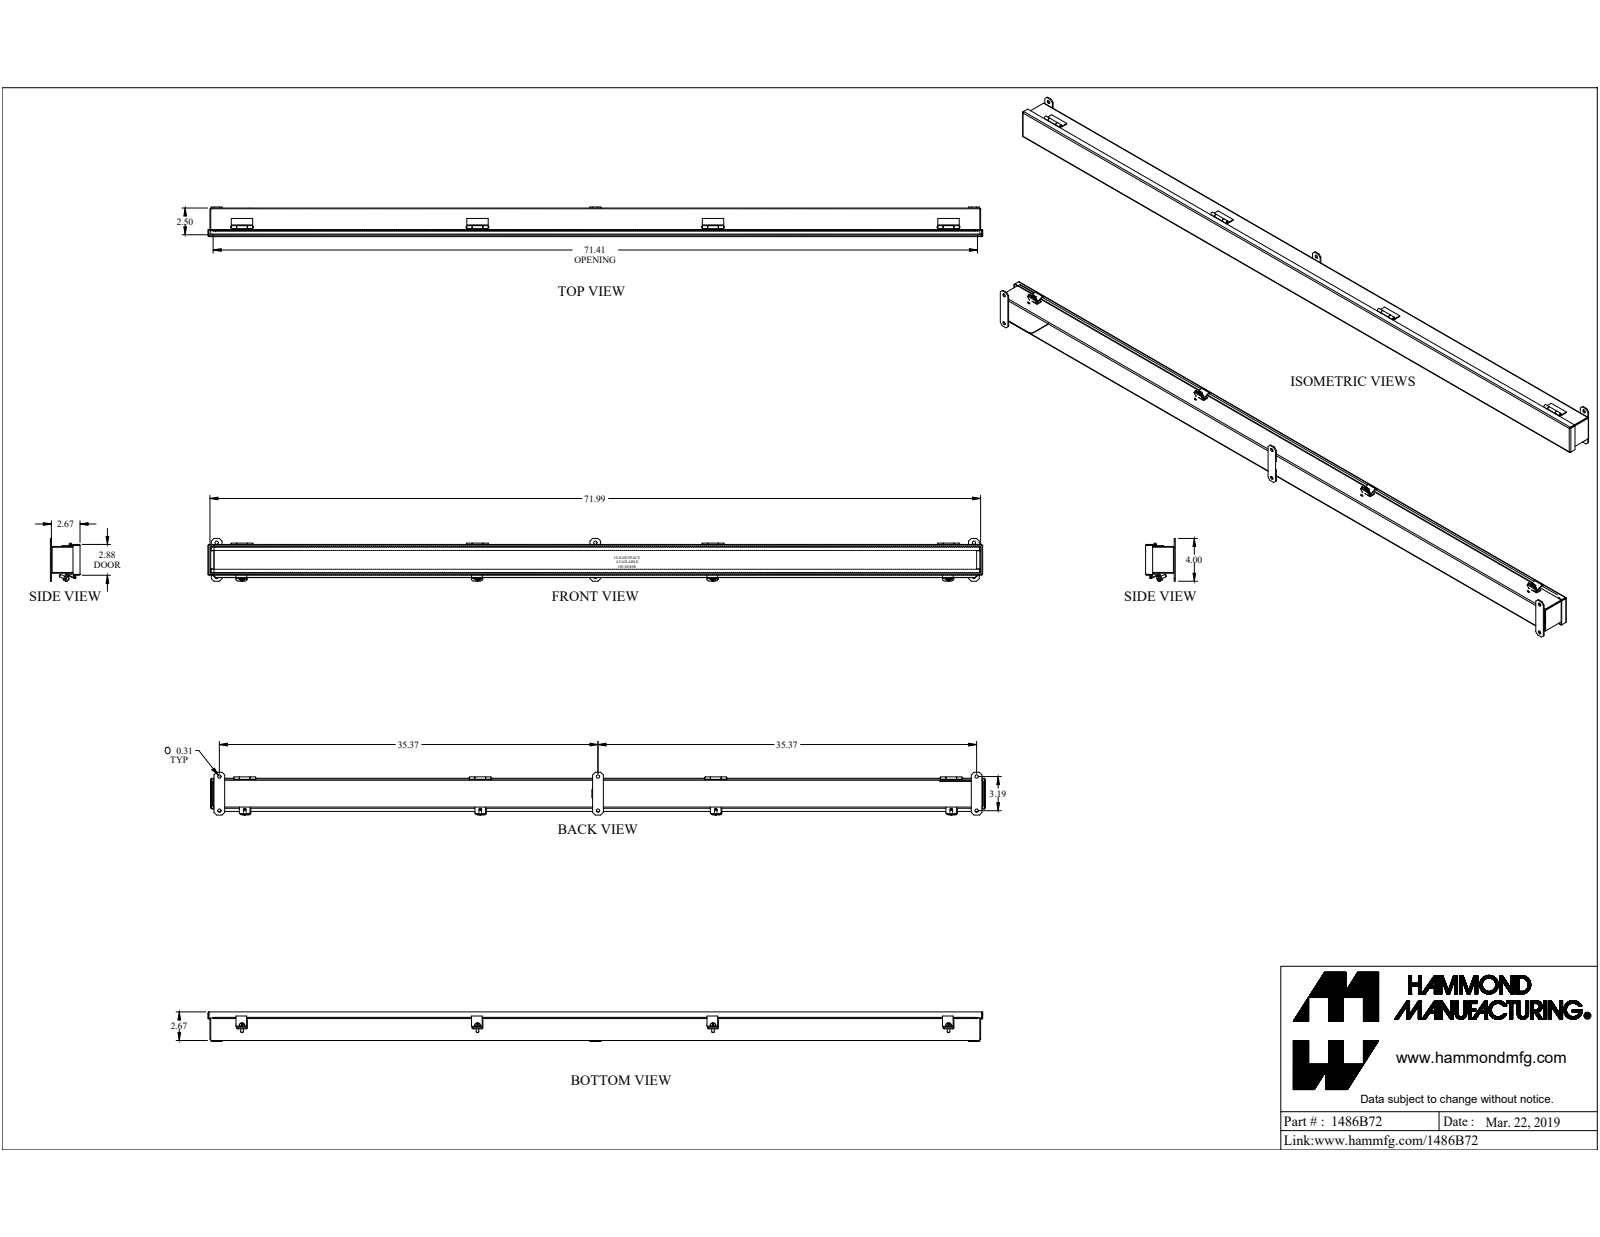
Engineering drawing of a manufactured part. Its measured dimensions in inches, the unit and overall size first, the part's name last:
Units: inches
Overall size (bounding box): 72.375 × 4.006 × 2.767
Round holes (diameter × count): ⌀0.313 ×6, ⌀0.213 ×4, ⌀0.125 ×1
Round bosses / shafts (diameter × count): ⌀0.48 ×5, ⌀0.246 ×5, ⌀0.275 ×1, ⌀0.125 ×1
Partial cylindrical surfaces — rounded edges, fillets, slot ends (radius × count): R0.188 ×18, R0.036 ×11, R0.108 ×11, R0.01 ×10, R0.141 ×10, R0.029 ×4, R0.086 ×4, R0.048 ×1
Main face-to-face distances: 0.072, 2.428, 2.6, 2.5, 2.356, 2.672, 2.528, 2.615, 0.187, 0.172
Hole centre spacings: 35.372, 35.515, 3.188, 22, 44, 70.744, 70.816, 66
Volume: 80.53 in³ · Surface area: 2 082 in²
Bodies: 37 solids, 696 faces (489 planar, 146 cylindrical, 61 other)
Part name (STEP PRODUCT): 1486B72
STEP written by: SolidWorks 2019 (CONFIG_CONTROL_DESIGN)
